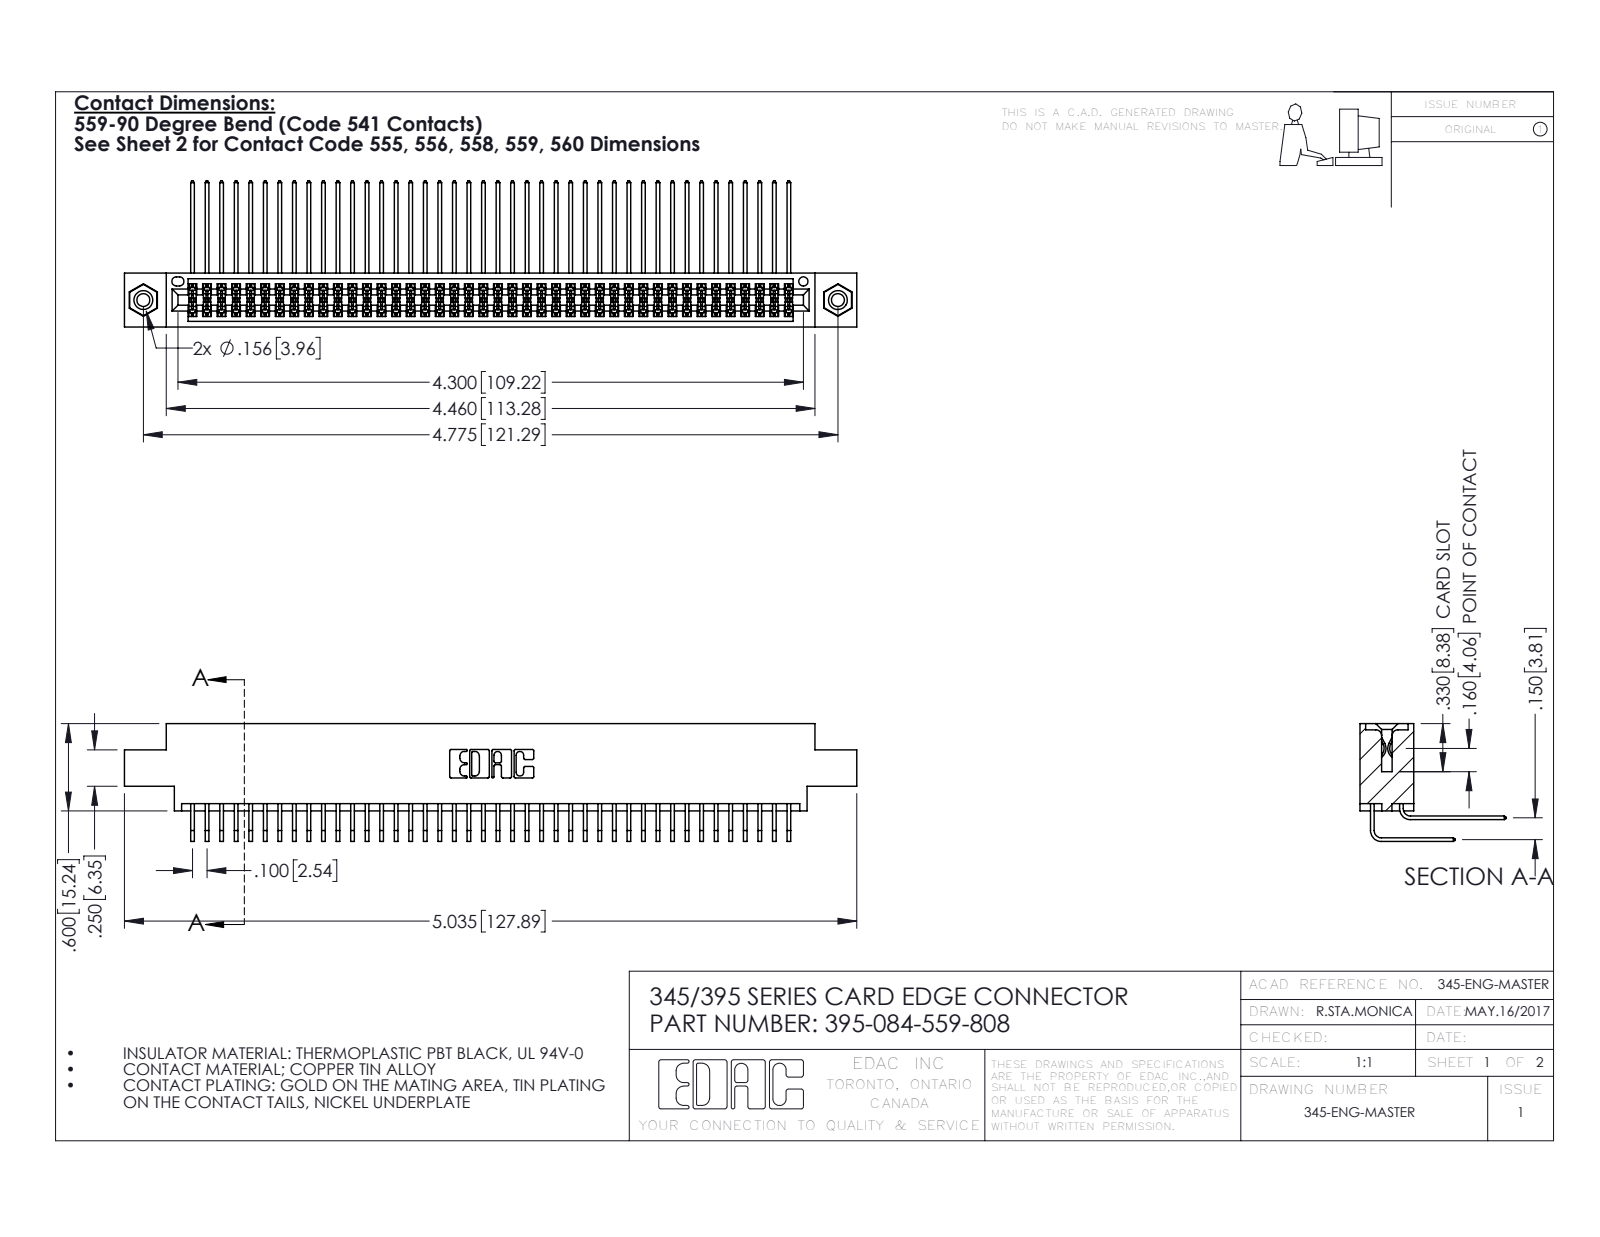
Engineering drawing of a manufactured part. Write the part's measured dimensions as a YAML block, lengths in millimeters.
part_name: "345-292-001_559 Tail - 2; 345-292-001_558 559 Tail - 1; 345 Part_0.170 Offset - 0.156 Dia-TI; 345-250-001_345-250-003-102 (+1 more)"
step_written_by: "SolidWorks 2016 (CONFIG_CONTROL_DESIGN)"
units: millimeters
bodies: {solids: 87, faces: 4558, planar: 3056, cylindrical: 1486, other: 16}
overall_size: [127.9, 25.5, 20.5]
volume: 12800
surface_area: 21340
round_holes:
  - {diameter: 2.3, count: 2}
  - {diameter: 3.2, count: 2}
  - {diameter: 4, count: 2}
  - {diameter: 1.6, count: 1}
round_bosses_or_shafts:
  - {diameter: 3.9, count: 2}
partial_cylinders:
  - {radius: 0.2, count: 126}
  - {radius: 0.3, count: 22}
  - {radius: 0.2, count: 6}
  - {radius: 0.8, count: 6}
  - {radius: 0.7, count: 3}
  - {radius: 0.4, count: 2}
  - {radius: 0.5, count: 2}
  - {radius: 0.6, count: 2}
face_to_face_distances: [1.8, 7.6, 5.1, 9.4, 2.5, 6.9, 0.6, 5.7, 4.4, 3.8]
hole_center_spacings: [6.9, 115.3, 121.3]
